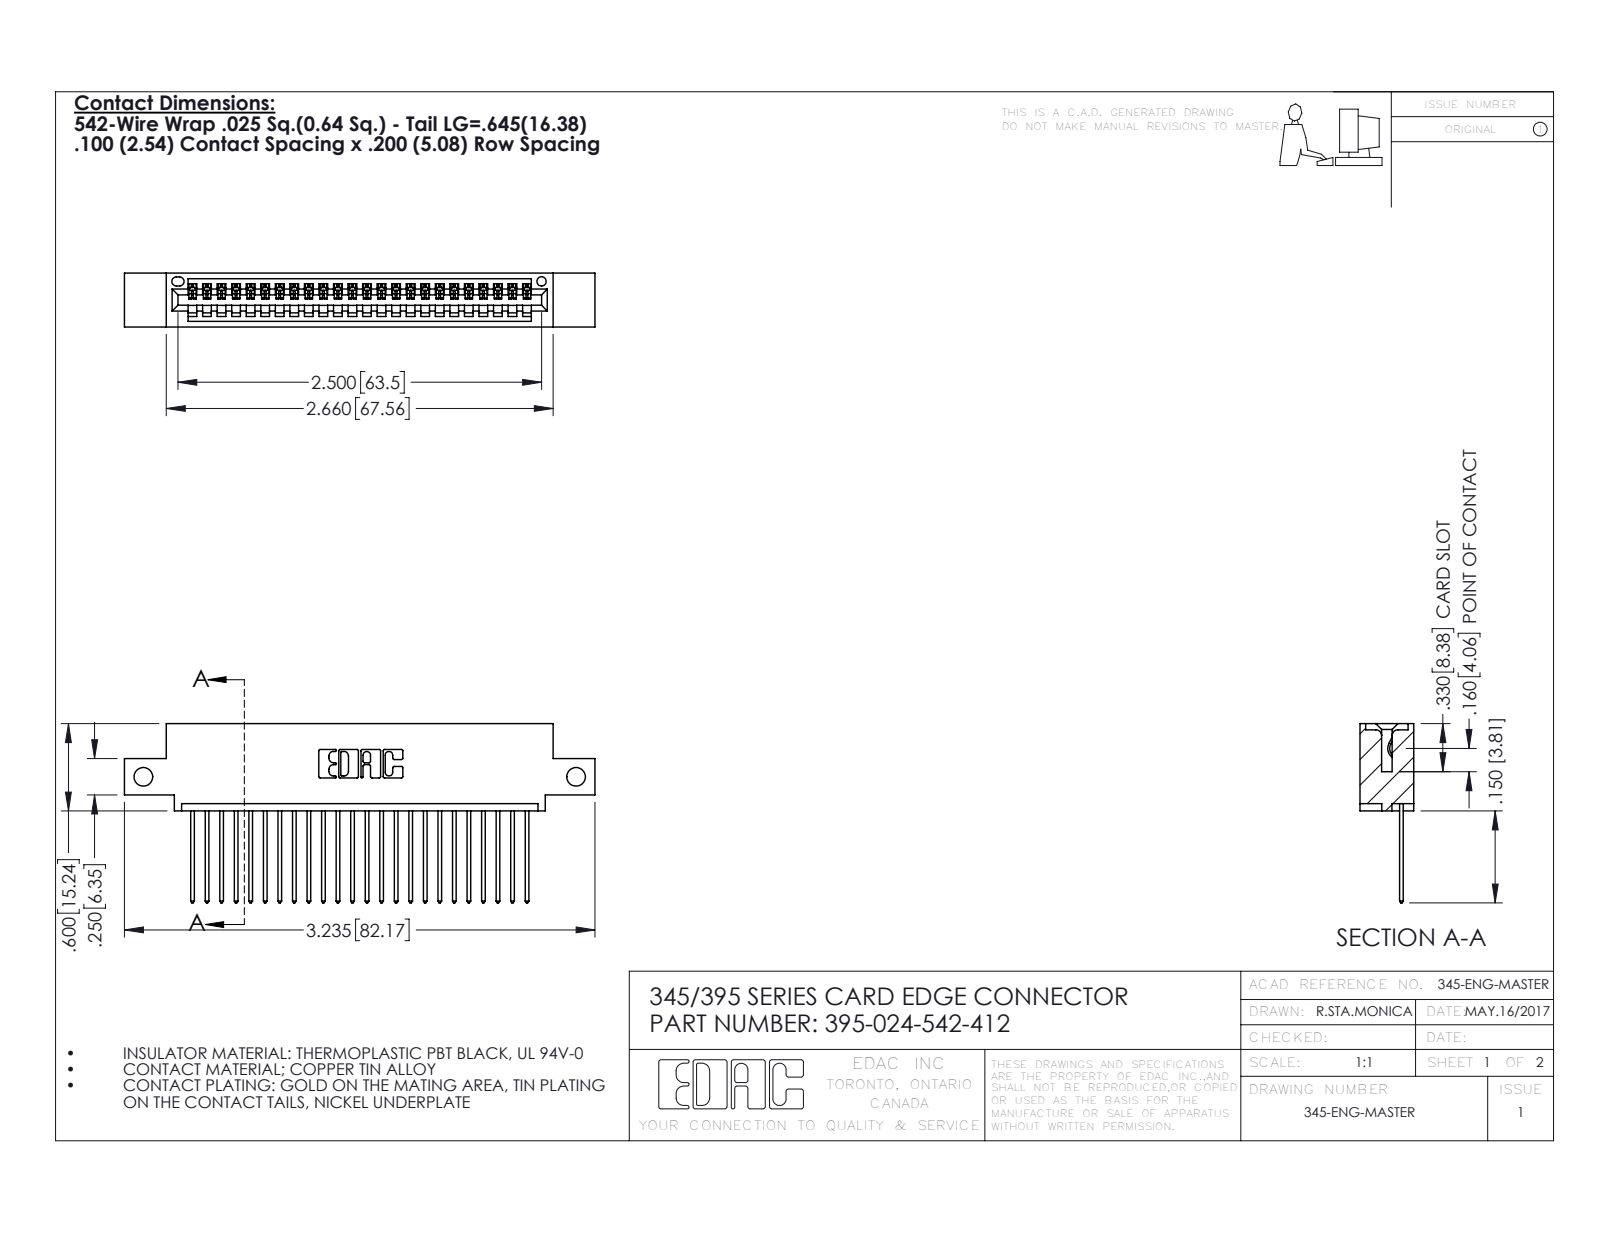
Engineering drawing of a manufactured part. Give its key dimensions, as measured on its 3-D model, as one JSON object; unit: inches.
{"part_name": "345 Part_0.110 Offset - Side Mount; 395-024-542-412; 345-292-001_345-293-142", "step_written_by": "SolidWorks 2016 (CONFIG_CONTROL_DESIGN)", "units": "inches", "bodies": {"solids": 25, "faces": 1522, "planar": 1044, "cylindrical": 478, "other": 0}, "overall_size": [3.235, 1.232, 0.37], "volume_in3": 0.461, "surface_area_in2": 15.6, "round_holes": [[0.128, 2], [0.064, 1]], "partial_cylinders_radius": [[0.006, 48], [0.01, 48], [0.01, 22], [0.007, 6], [0.031, 6], [0.026, 3], [0.031, 2], [0.04, 2]], "face_to_face_distances": [0.298, 0.072, 0.37, 0.2, 0.098, 0.272, 0.025, 0.225, 0.149, 0.072], "hole_center_spacings": [2.975]}
